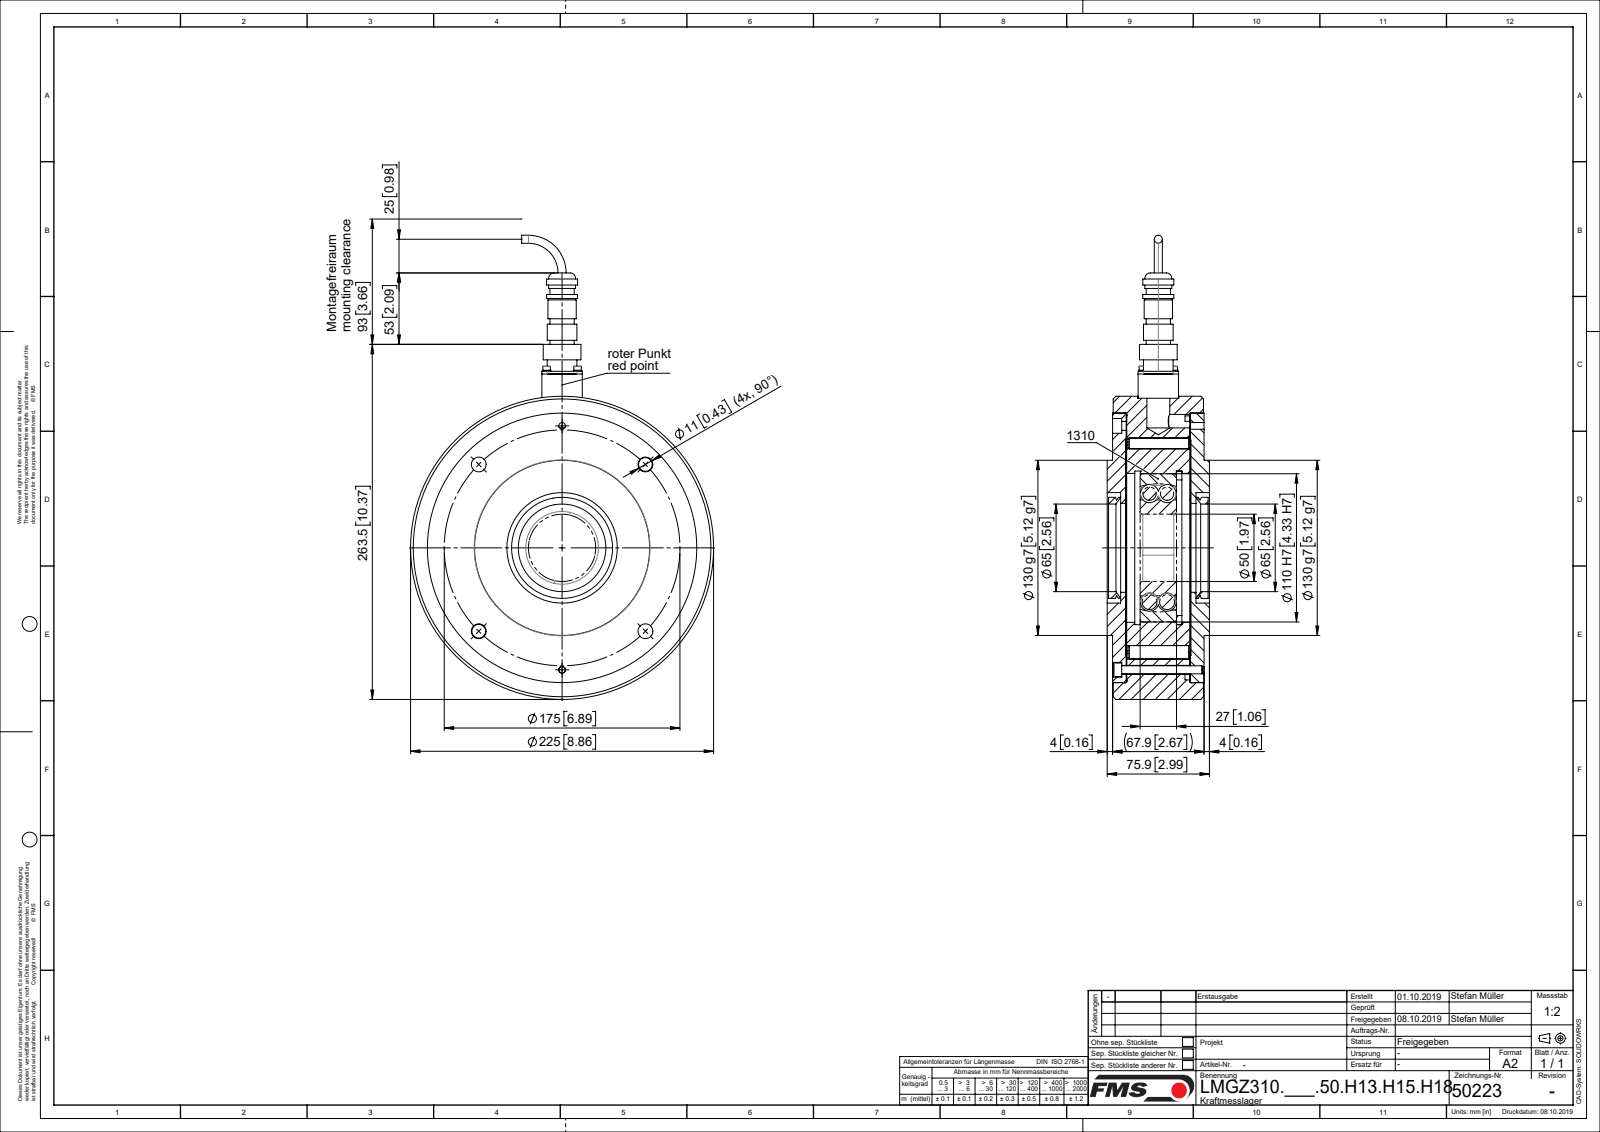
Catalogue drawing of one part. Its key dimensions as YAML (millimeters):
part_name: "ZEICHNUNG7; L50223; L49152; TEIL1 (+8 more)"
step_written_by: "Mechanical Desktop 2007 (CONFIG_CONTROL_DESIGN)"
units: millimeters
bodies: {solids: 20, faces: 392, planar: 98, cylindrical: 234, other: 60}
overall_size: [344.5, 225, 75.9]
volume: 2420000
surface_area: 390313
round_holes:
  - {diameter: 11, count: 6}
  - {diameter: 2.6, count: 4}
  - {diameter: 3.2, count: 4}
  - {diameter: 3.4, count: 4}
  - {diameter: 9, count: 4}
  - {diameter: 5, count: 2}
  - {diameter: 6.6, count: 2}
  - {diameter: 50, count: 1}
  - {diameter: 64, count: 1}
  - {diameter: 66, count: 1}
  - {diameter: 82, count: 1}
  - {diameter: 88.2, count: 1}
round_bosses_or_shafts:
  - {diameter: 6.2, count: 4}
  - {diameter: 5.5, count: 4}
  - {diameter: 3, count: 4}
  - {diameter: 2.5, count: 4}
  - {diameter: 6, count: 2}
  - {diameter: 225, count: 1}
  - {diameter: 199, count: 1}
  - {diameter: 130, count: 1}
partial_cylinders:
  - {radius: 4, count: 4}
  - {radius: 81, count: 1}
  - {radius: 86, count: 1}
face_to_face_distances: [9.7, 47.25, 10.45, 10.75, 47.45, 57.7, 10.2, 57.45, 47, 10]
hole_center_spacings: [23, 87.5, 32.53, 68.17, 68.18, 90.5, 123.74, 123.75]
